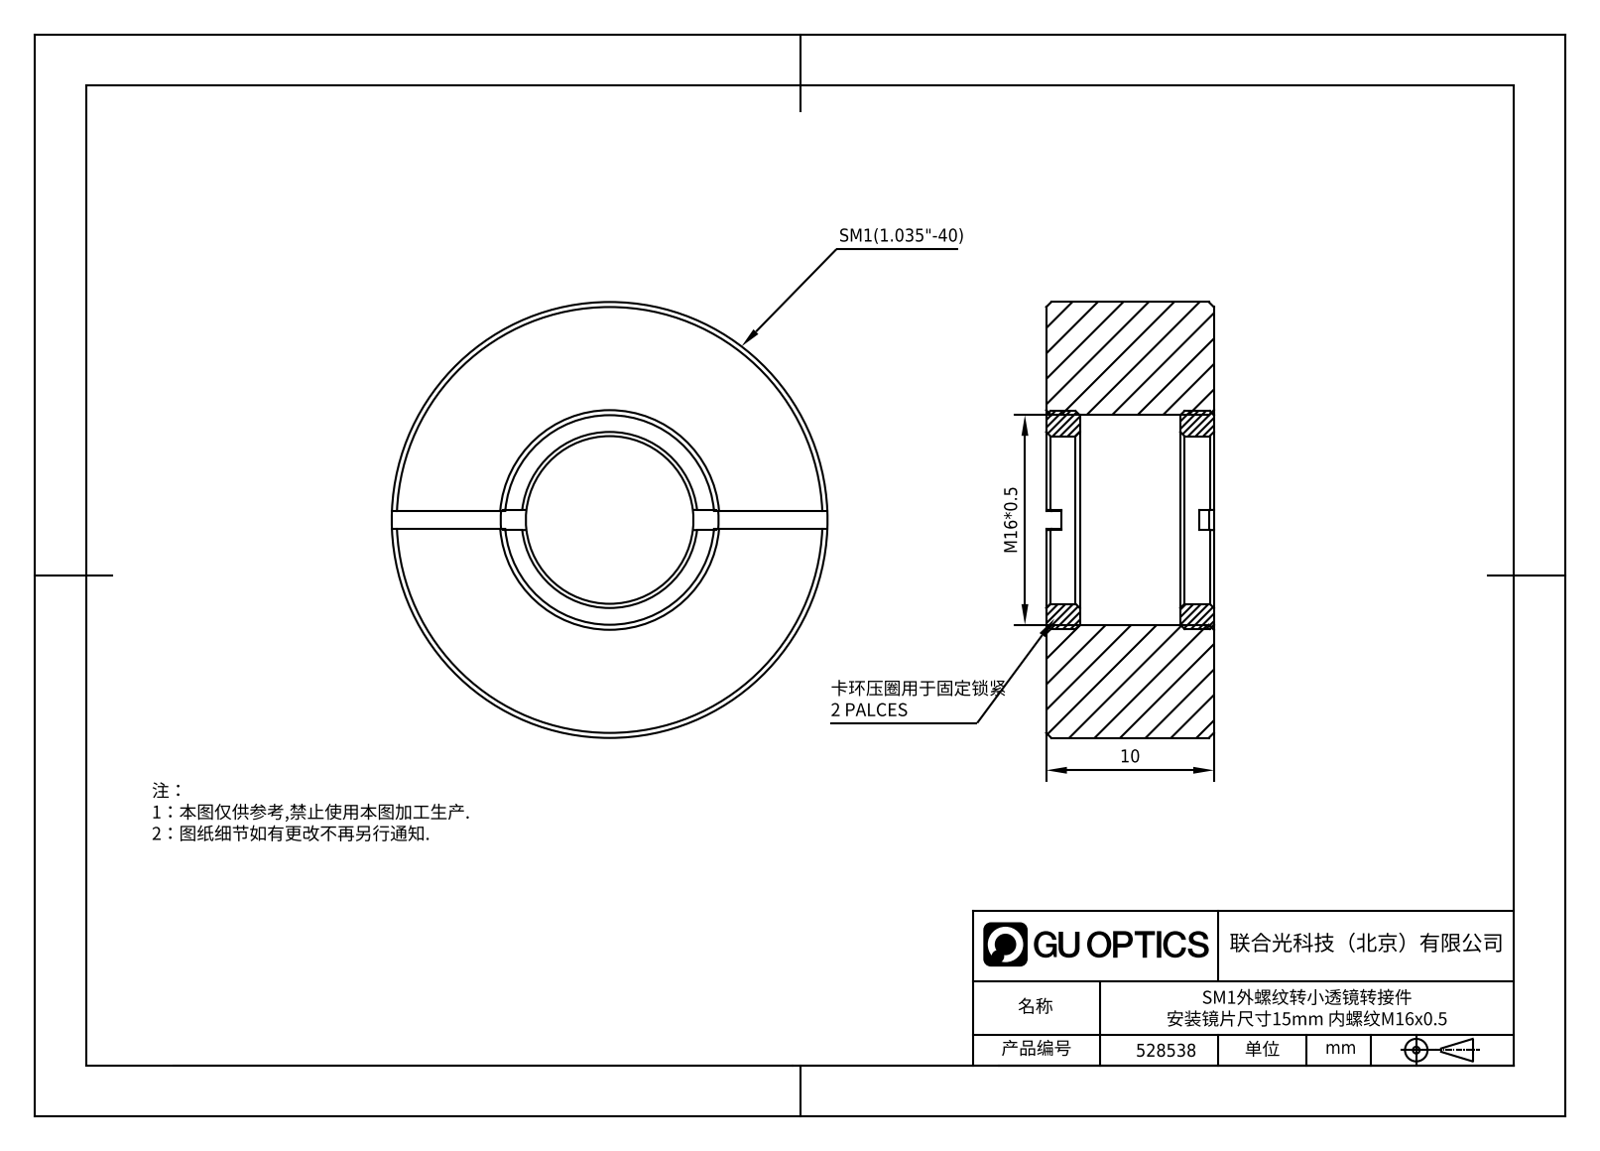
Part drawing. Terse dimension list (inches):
name: 528538
written by: SolidWorks 2020 (CONFIG_CONTROL_DESIGN)
unit: in
bodies: 3 solids, 51 faces (27 planar, 6 cylindrical, 18 other)
size: 1.024 × 1.024 × 0.394
volume: 0.223 in³; area: 3.948 in²
holes: 1× ⌀0.512, 1× ⌀0.61
bosses: 1× ⌀1.024, 1× ⌀0.63
face distances: 0.394, 0.079, 0.315, 0.236, 0.039, 0.043, 0.354, 0.276, 0.045, 0.035
